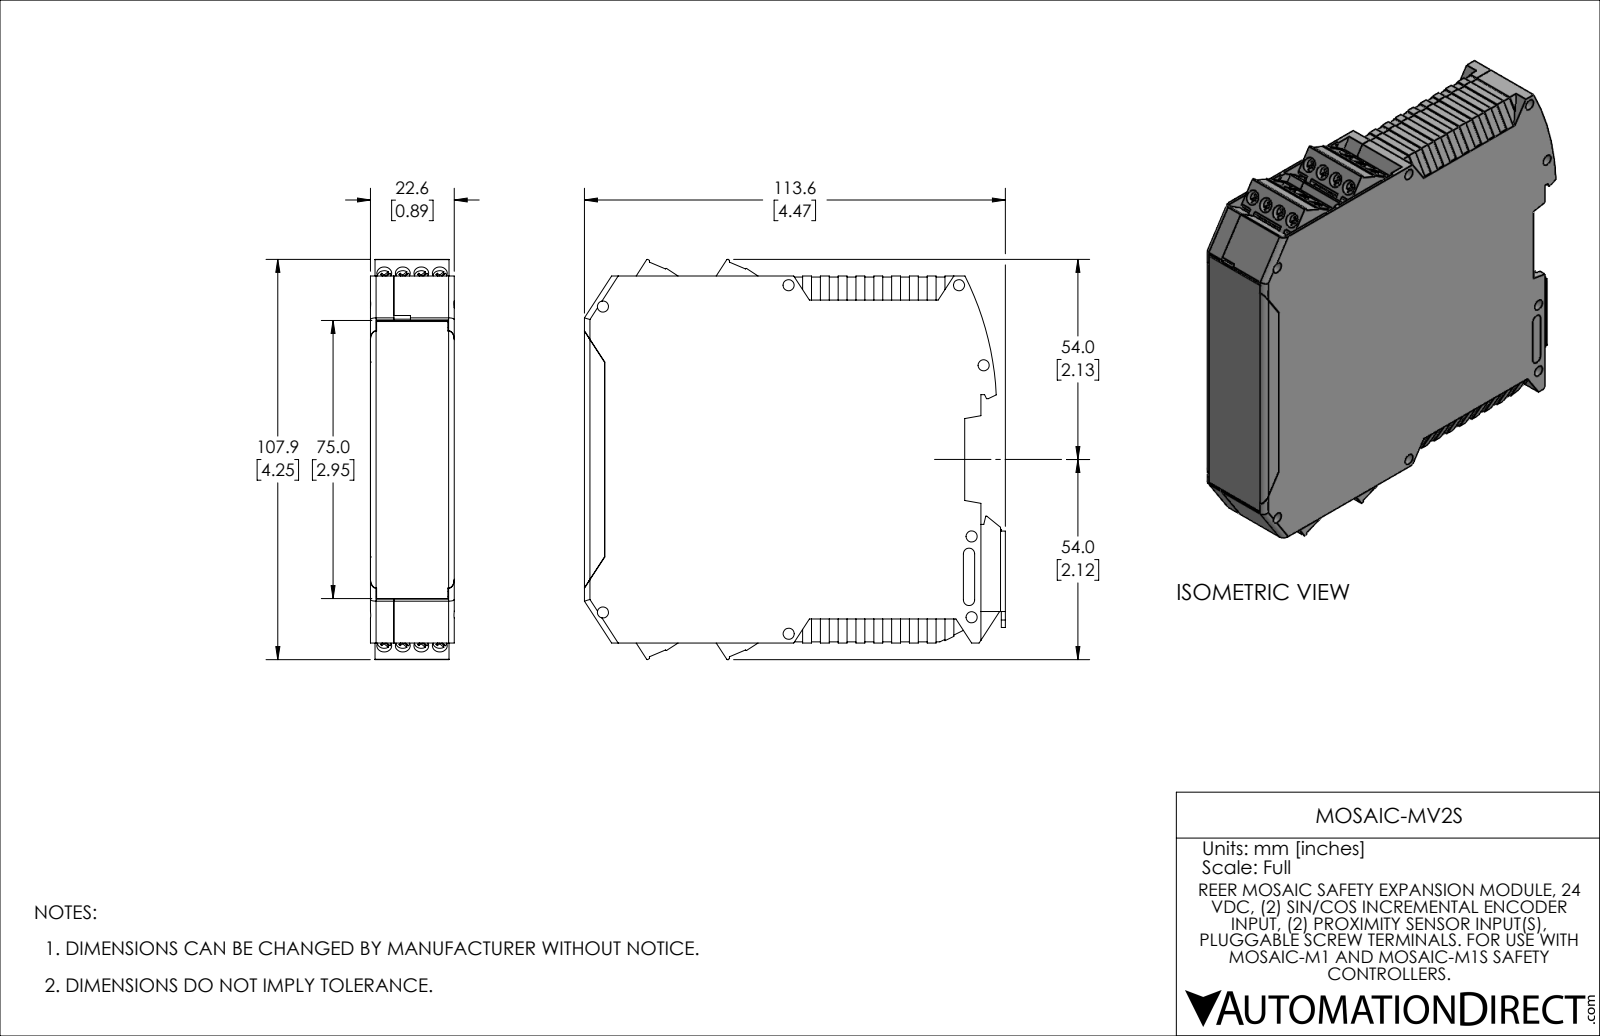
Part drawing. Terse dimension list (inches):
name: MOSAIC-MV2S
written by: SolidWorks 2021 (AUTOMOTIVE_DESIGN)
unit: in
bodies: 9 solids, 1954 faces (1569 planar, 379 cylindrical, 6 other)
size: 4.472 × 4.25 × 0.89
volume: 3.484 in³; area: 117.5 in²
holes: 18× ⌀0.055, 16× ⌀0.11, 16× ⌀0.157, 14× ⌀0.118, 1× ⌀0.063
bosses: 16× ⌀0.149, 1× ⌀0.177, 1× ⌀0.11, 1× ⌀0.053
rounds: 33× R0.012, 16× R0.114, 12× R0.008, 12× R0.03, 8× R0.059, 6× R0.031, 5× R0.098, 4× R0.024
face distances: 0.049, 0.841, 0.89, 0.791, 0.039, 0.248, 0.047, 0.199, 0.593, 0.642
hole spacings: 0.197, 0.394, 0.591, 0.503, 0.504, 0.74, 0.74, 0.463
